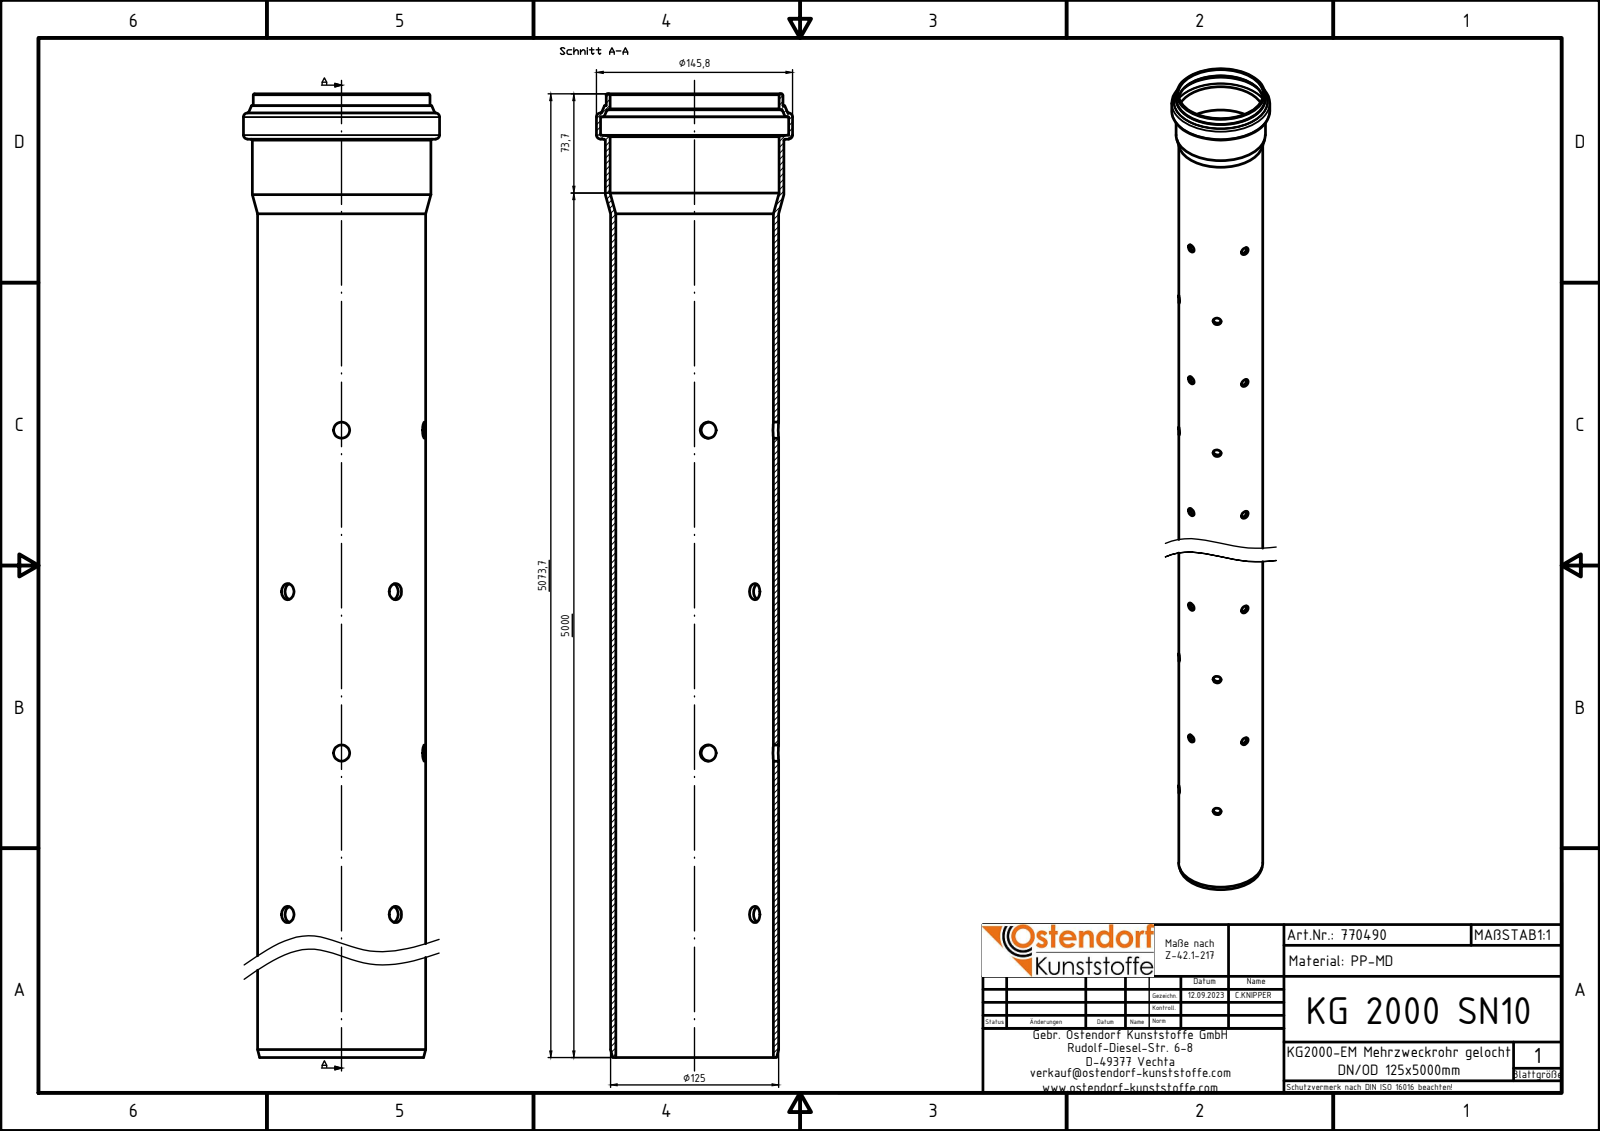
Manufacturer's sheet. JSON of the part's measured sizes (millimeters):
{"part_name": "770490z", "step_written_by": "Autodesk Inventor 2024 (AUTOMOTIVE_DESIGN)", "units": "millimeters", "bodies": {"solids": 1, "faces": 115, "planar": 5, "cylindrical": 88, "other": 22}, "overall_size": [5073.7, 145.8, 145.8], "volume_mm3": 7497000, "surface_area_mm2": 3870000, "round_holes": [[12, 80], [117.2, 1], [125.5, 1], [139.8, 1]], "round_bosses_or_shafts": [[145.8, 1], [132.7, 1], [131.5, 1], [125, 1]], "face_to_face_distances": [5040, 5073.7, 33.7, 5064.87, 24.87, 8.83, 5059.5, 19.5, 5.37, 14.2], "hole_center_spacings": [240, 480, 720, 960, 1200, 1440, 1680, 1920]}
